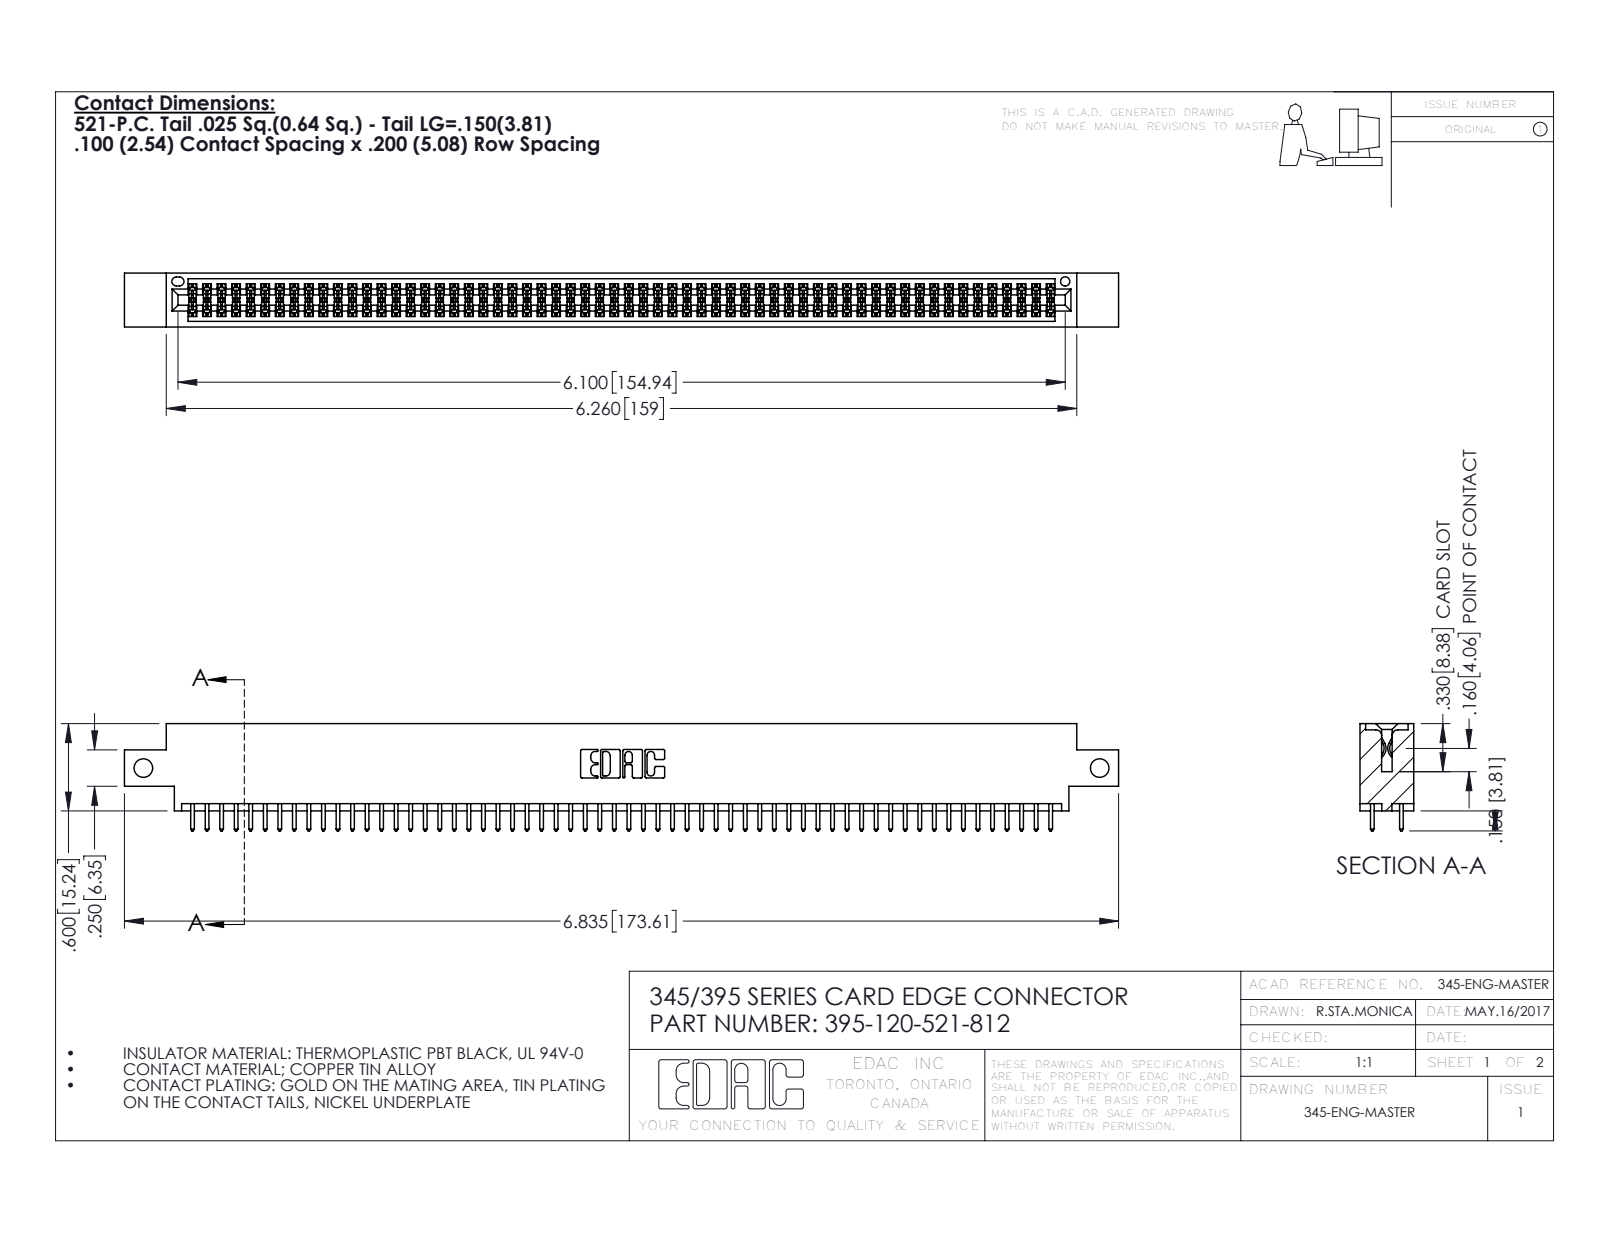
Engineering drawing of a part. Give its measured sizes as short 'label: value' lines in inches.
name: 395-120-521-812; 345-292-001_345-293-121; 345 Part_0.170 Offset - Side Mount
written by: SolidWorks 2016 (CONFIG_CONTROL_DESIGN)
unit: in
bodies: 121 solids, 6130 faces (4044 planar, 2086 cylindrical, 0 other)
size: 6.835 × 0.737 × 0.37
volume: 1.024 in³; area: 38.51 in²
holes: 2× ⌀0.128, 1× ⌀0.064
rounds: 180× R0.006, 120× R0.01, 22× R0.01, 6× R0.007, 6× R0.031, 3× R0.026, 2× R0.014, 2× R0.019
face distances: 0.298, 0.072, 0.2, 0.37, 0.098, 0.272, 0.025, 0.225, 0.175, 0.149
hole spacings: 6.575
